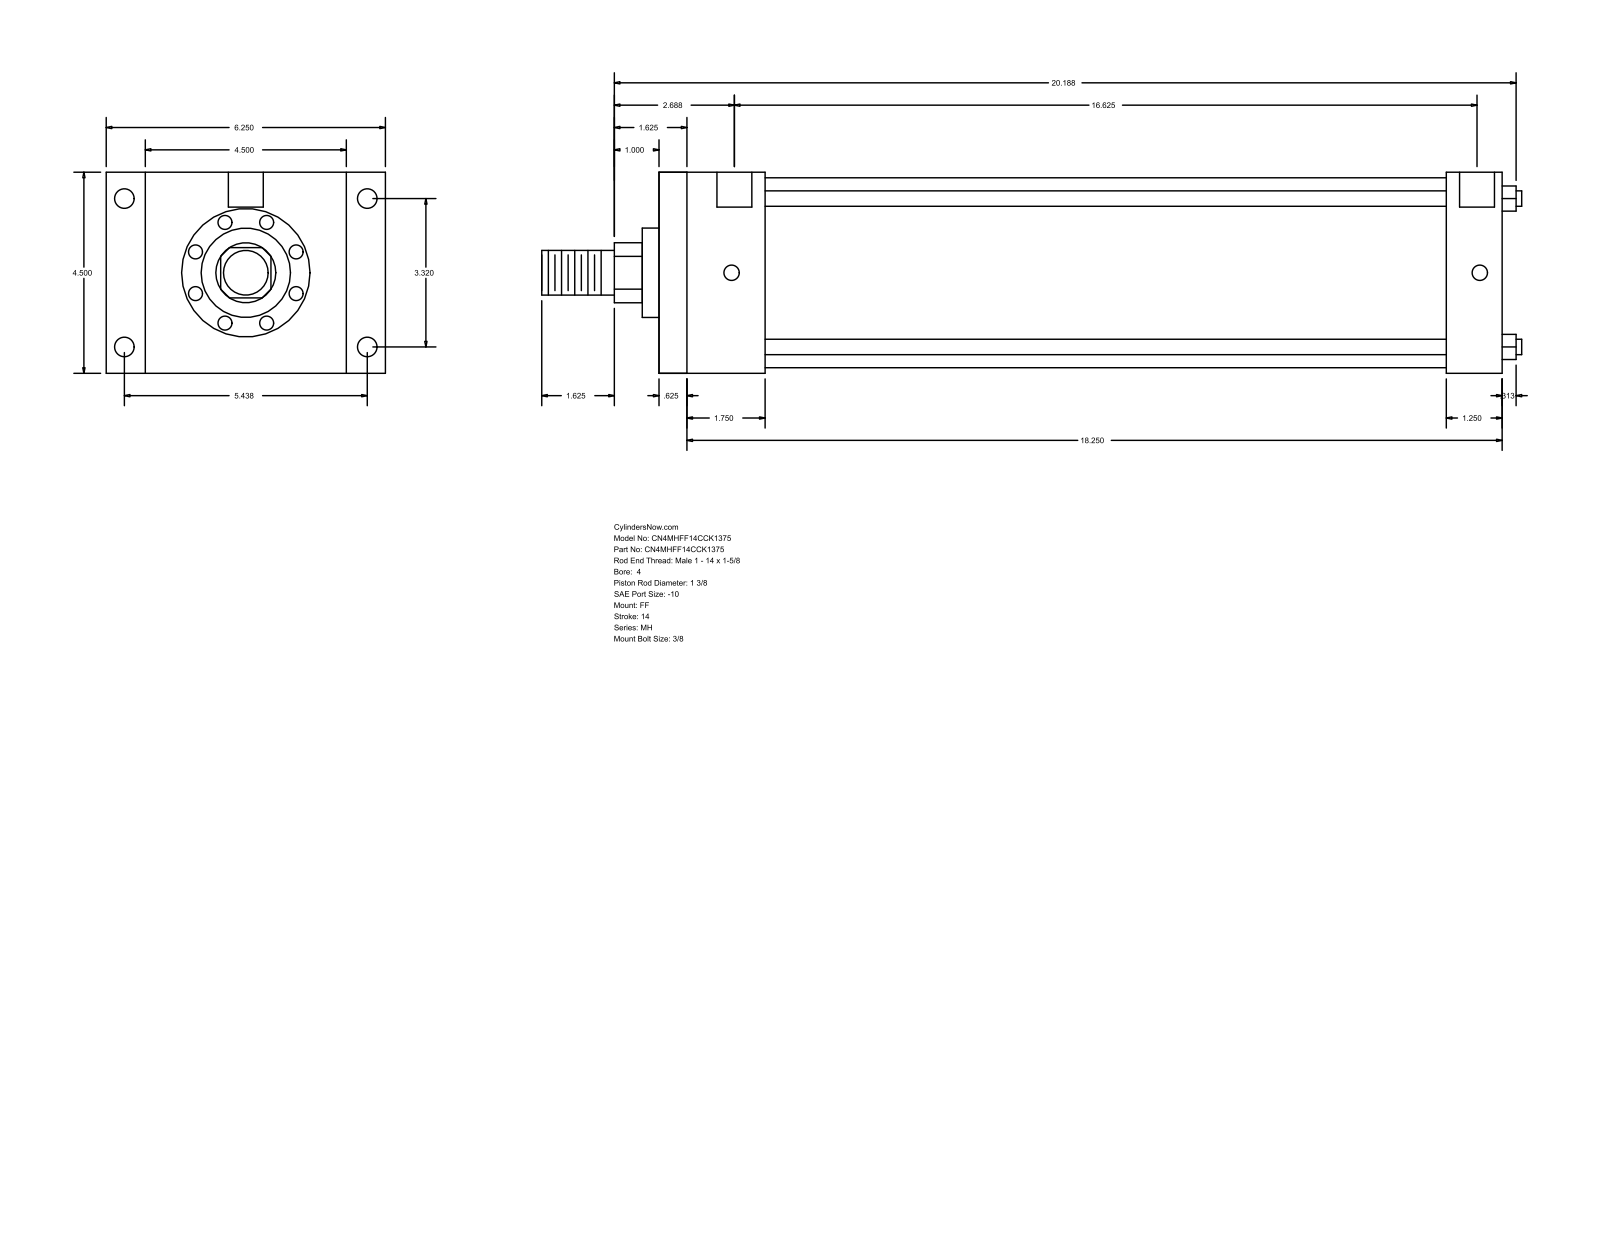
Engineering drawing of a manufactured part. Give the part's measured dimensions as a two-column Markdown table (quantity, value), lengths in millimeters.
| quantity | value |
| --- | --- |
| part name | MH_FF__0400_1.375 |
| STEP written by | GSSL Pune (CONFIG_CONTROL_DESIGN) |
| units | millimeters |
| bodies | 0 solids, 92 faces (64 planar, 28 cylindrical, 0 other) |
| overall size | 557.21 × 158.75 × 114.3 |
| round holes (diameter × count) | 8.73 × 4, 11.13 × 4, 19.84 × 2 |
| round bosses / shafts (diameter × count) | 8.76 × 4, 107.95 × 1, 50.8 × 1, 34.92 × 1, 25.4 × 1 |
| partial cylindrical surfaces (radius × count) | 17.06 × 1 |
| main face-to-face distances | 114.3, 479.42, 15.87, 463.55, 60.32, 44.45, 419.1, 447.67, 431.8, 387.35 |
| hole center spacings | 84.32, 138.12, 161.82, 425.45, 1.58, 1.59, 422.28, 423.86 |
